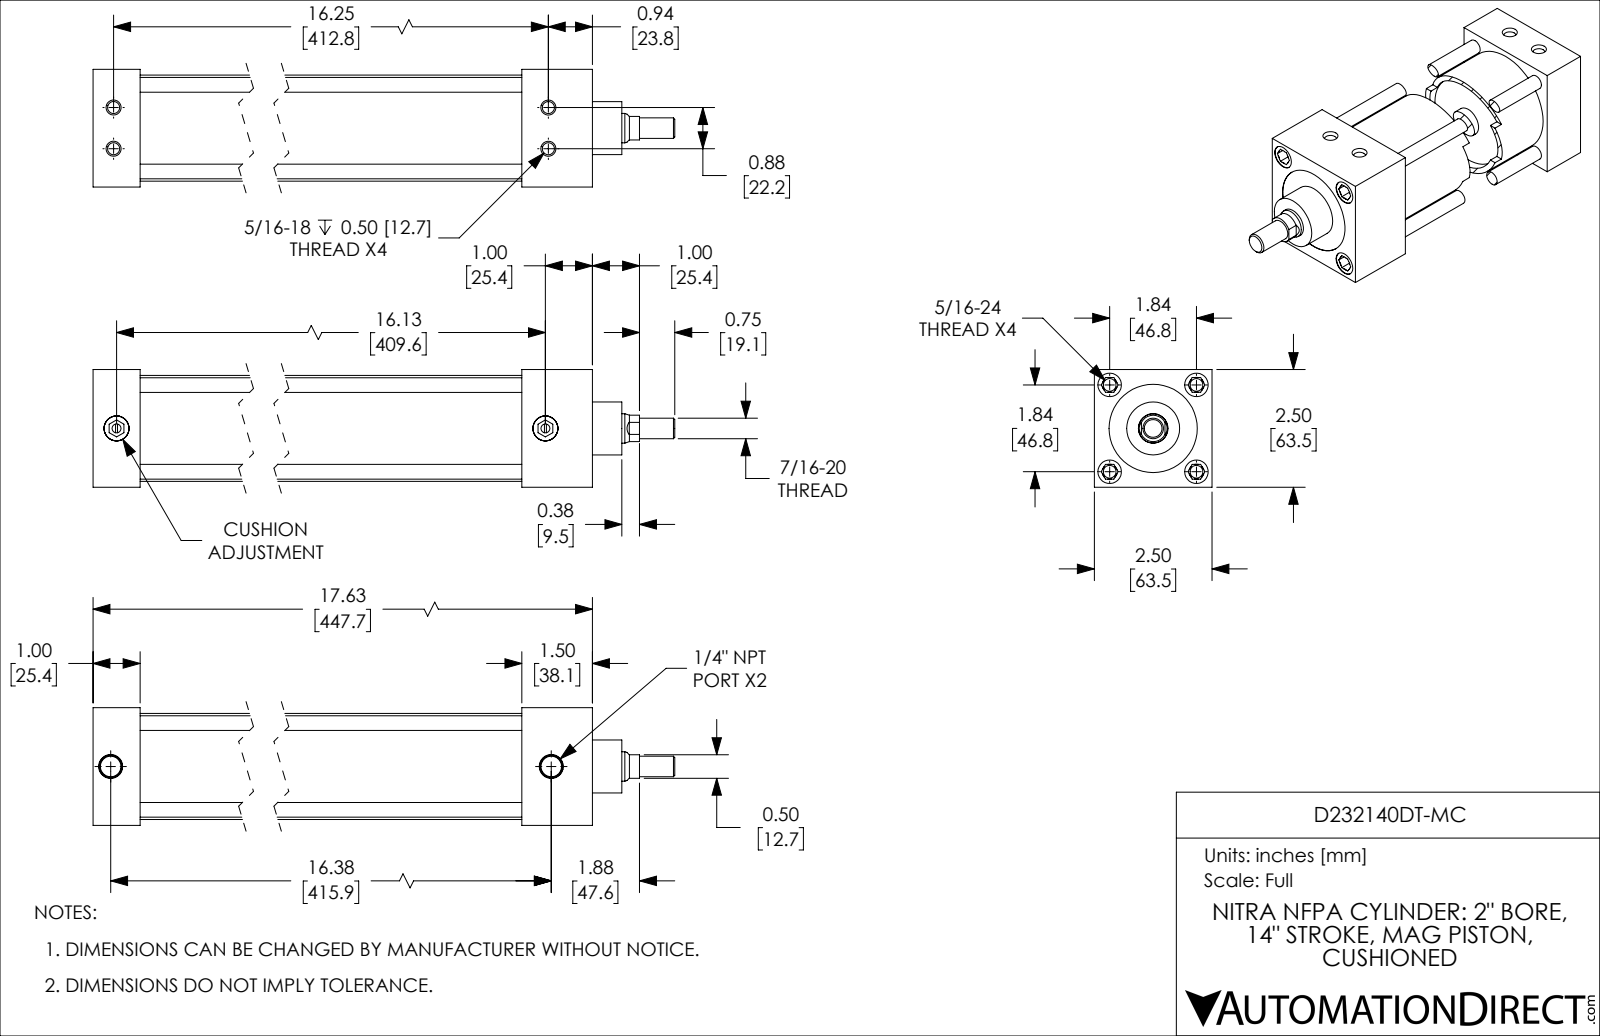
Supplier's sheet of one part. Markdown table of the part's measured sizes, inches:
| quantity | value |
| --- | --- |
| part name | D232140DT-MC_PISTON_KK1; D232140DT-MC_CUSHION; D232140DT-MC_BODY; D232140DT-MC |
| STEP written by | SolidWorks 2019 (CONFIG_CONTROL_DESIGN) |
| units | inches |
| bodies | 4 solids, 248 faces (90 planar, 78 cylindrical, 80 other) |
| overall size | 19.375 × 2.5 × 2.5 |
| volume | 40.68 in³ |
| surface area | 373.3 in² |
| round holes (diameter × count) | 0.272 × 7, 0.257 × 4, 0.5 × 4, 0.19 × 2, 0.438 × 2, 0.531 × 2, 0.626 × 1, 1.875 × 1, 2.001 × 1 |
| round bosses / shafts (diameter × count) | 0.312 × 4, 0.532 × 2, 2.251 × 1, 1.999 × 1, 1.125 × 1, 0.624 × 1, 0.437 × 1 |
| partial cylindrical surfaces (radius × count) | 0.281 × 1 |
| main face-to-face distances | 2.5, 1, 16.125, 15.125, 1.125, 2.125, 14, 1.5, 17.625, 16.625 |
| hole center spacings | 1.84, 1.844, 1.301, 0.441, 0.443, 0.875, 1.304, 2.602 |
